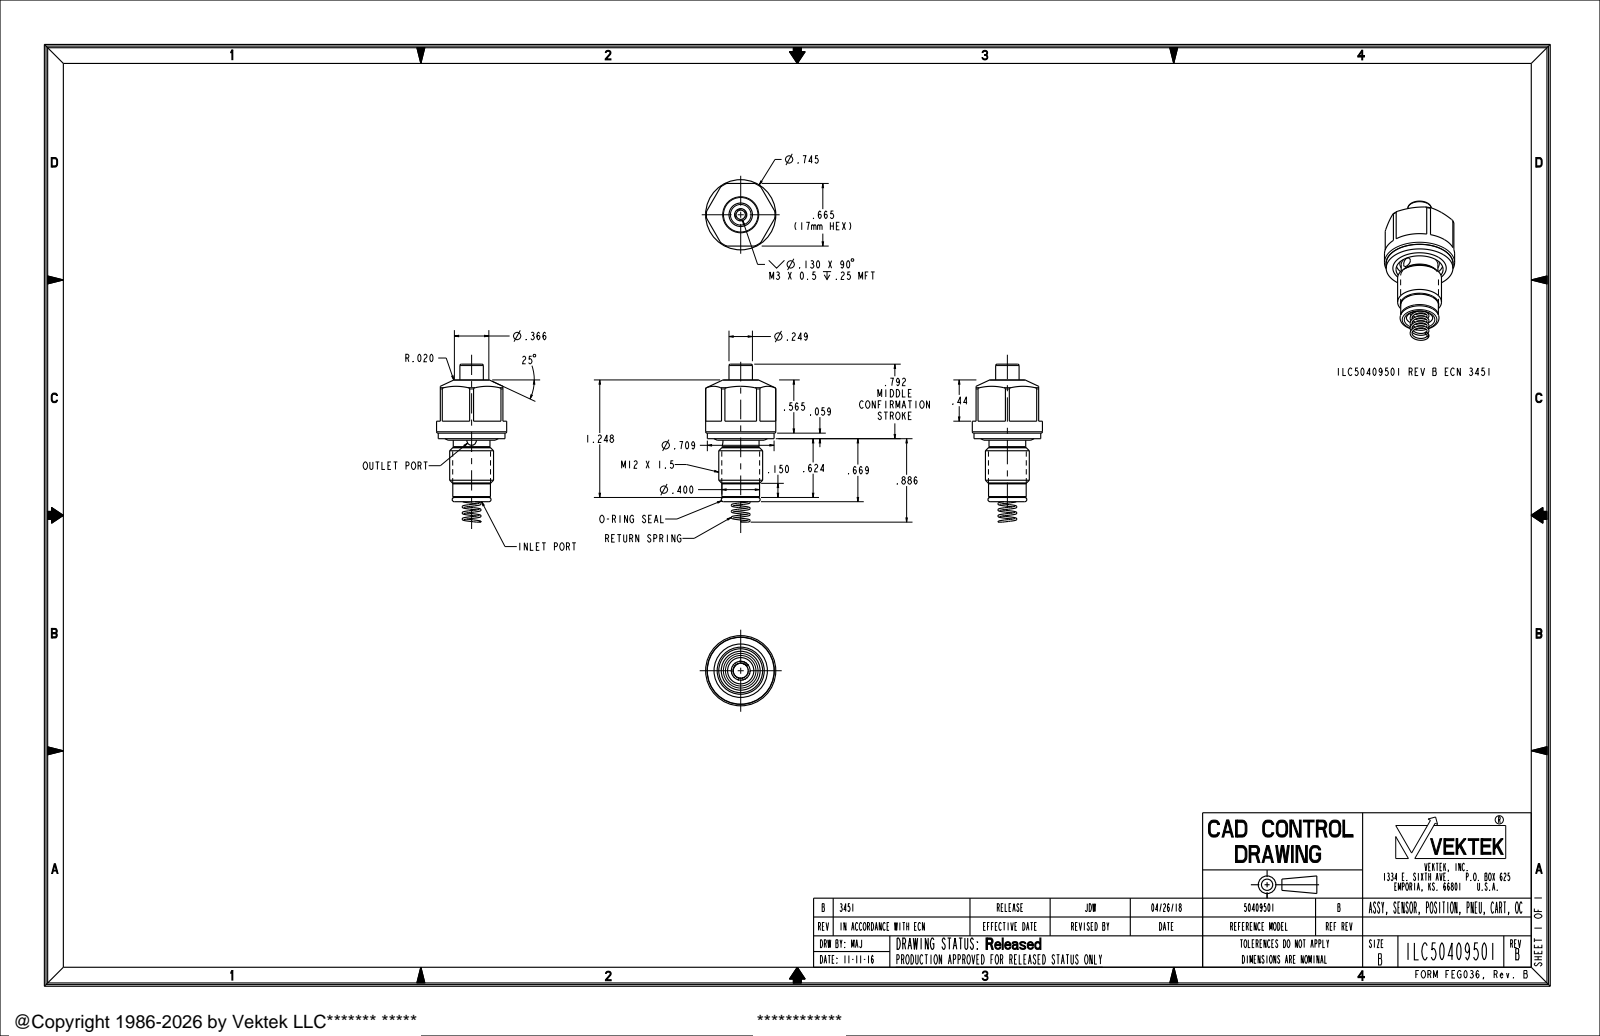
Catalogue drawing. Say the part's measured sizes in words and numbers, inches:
The part is named "ILC50409501". Its 3-D file was written by "PRO/ENGINEER BY PARAMETRIC TECHNOLOGY CORPORATION, 2013320 (AUTOMOTIVE_DESIGN)". It is 1 solid with 92 faces: 26 planar, 24 cylindrical and 42 other. Overall it measures 1.678 by 0.745 by 0.745 inches. Its volume is 0.308 cubic inches and its surface area 4.847 square inches. Round holes: 1 of diameter 0.098, 1 of diameter 0.1, 1 of diameter 0.118, 1 of diameter 0.312, 1 of diameter 0.5. Round bosses or shafts: 1 of diameter 0.745, 1 of diameter 0.709, 1 of diameter 0.466, 1 of diameter 0.402, 1 of diameter 0.4, 1 of diameter 0.39, 1 of diameter 0.249. The main face-to-face distances are 0.665, 0.324, 0.624, 0.383, 0.059, 0.948, 0.565, 0.51, 0.186, 0.127.
